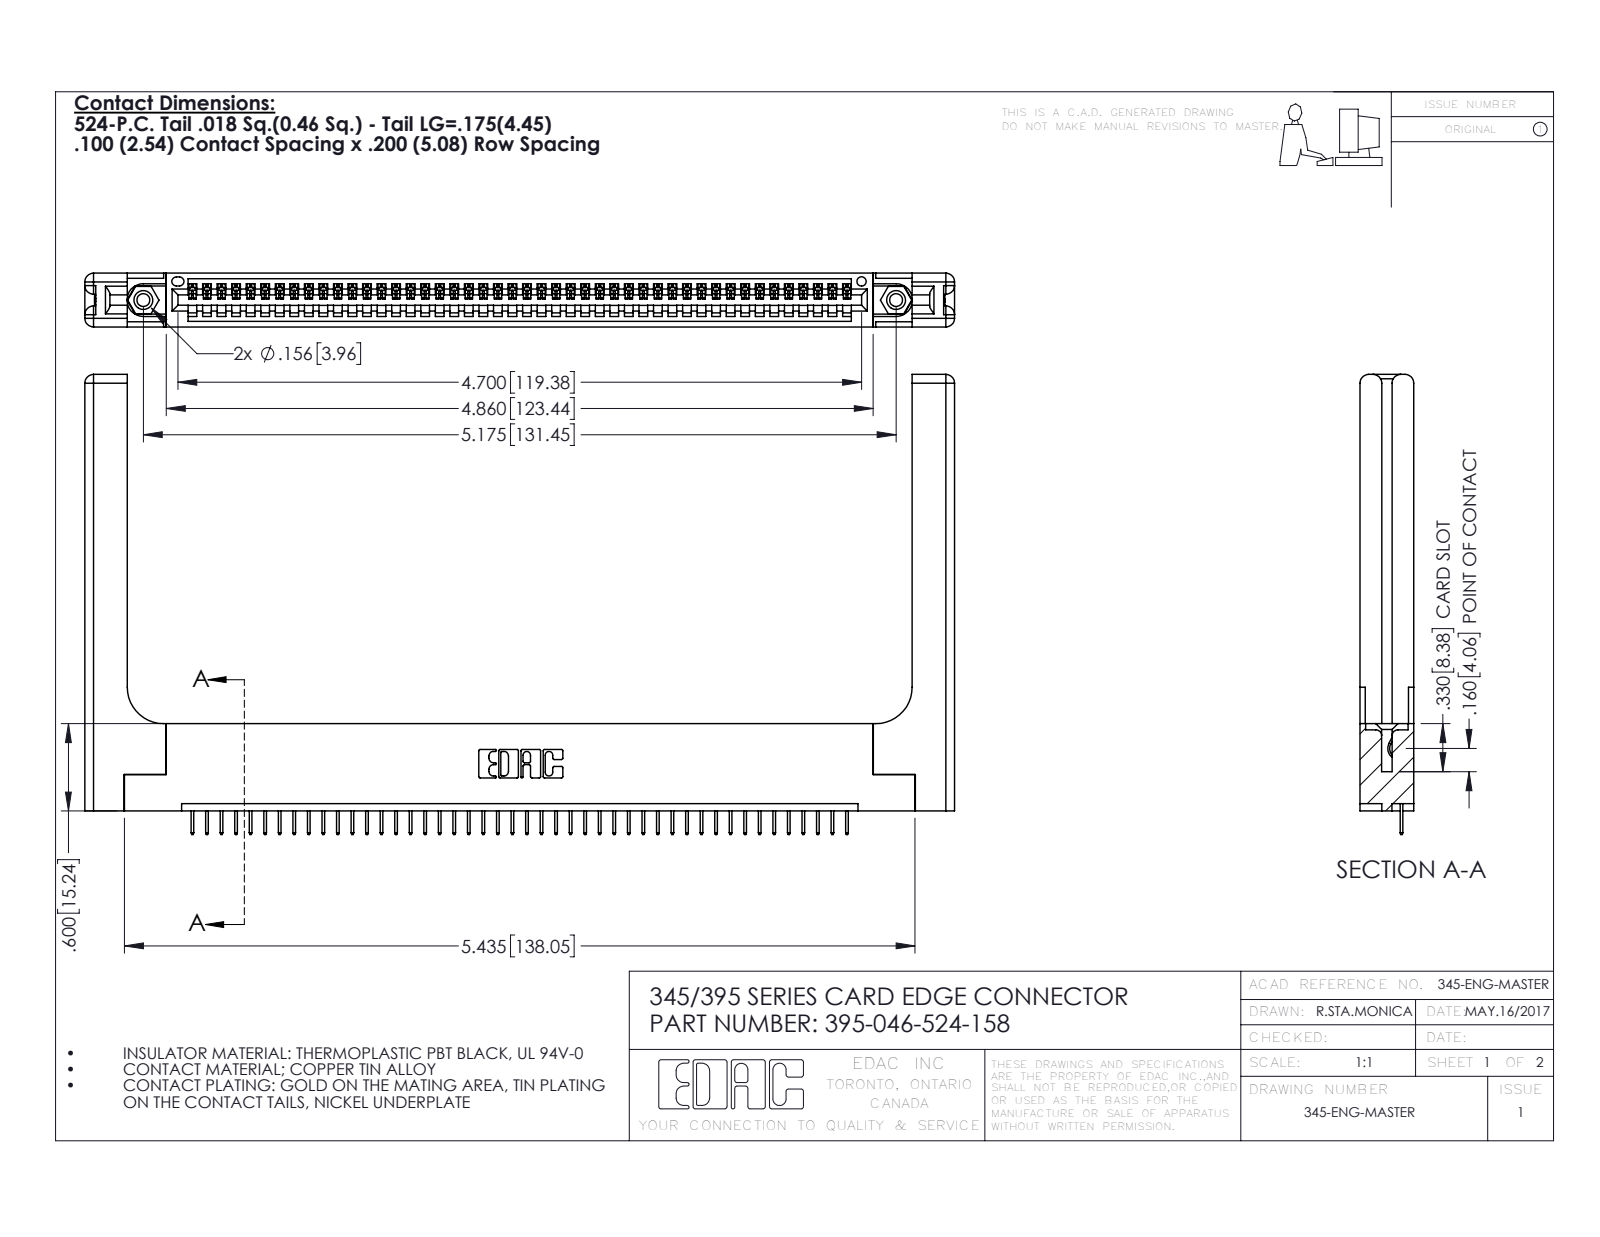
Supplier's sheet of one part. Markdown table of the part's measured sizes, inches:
| quantity | value |
| --- | --- |
| part name | 345-292-001_345-293-124; 395-046-524-158; 345 Part_Flush Mounting Lugs - 0.156 Dia-TH; 345-220-058_345-220-058 (+1 more) |
| STEP written by | SolidWorks 2016 (CONFIG_CONTROL_DESIGN) |
| units | inches |
| bodies | 51 solids, 3234 faces (2344 planar, 830 cylindrical, 60 other) |
| overall size | 5.979 × 3.162 × 0.37 |
| volume | 1.39 in³ |
| surface area | 36.81 in² |
| round holes (diameter × count) | 0.089 × 2, 0.125 × 2, 0.156 × 2, 0.064 × 1 |
| round bosses / shafts (diameter × count) | 0.155 × 2 |
| partial cylindrical surfaces (radius × count) | 0.006 × 92, 0.01 × 22, 0.06 × 16, 0.007 × 6, 0.031 × 6, 0.026 × 3, 0.03 × 2, 0.031 × 2 |
| main face-to-face distances | 0.37, 0.072, 0.298, 0.2, 0.098, 0.272, 0.025, 0.225, 0.148, 0.15 |
| hole center spacings | 0.27, 4.939, 5.175 |
